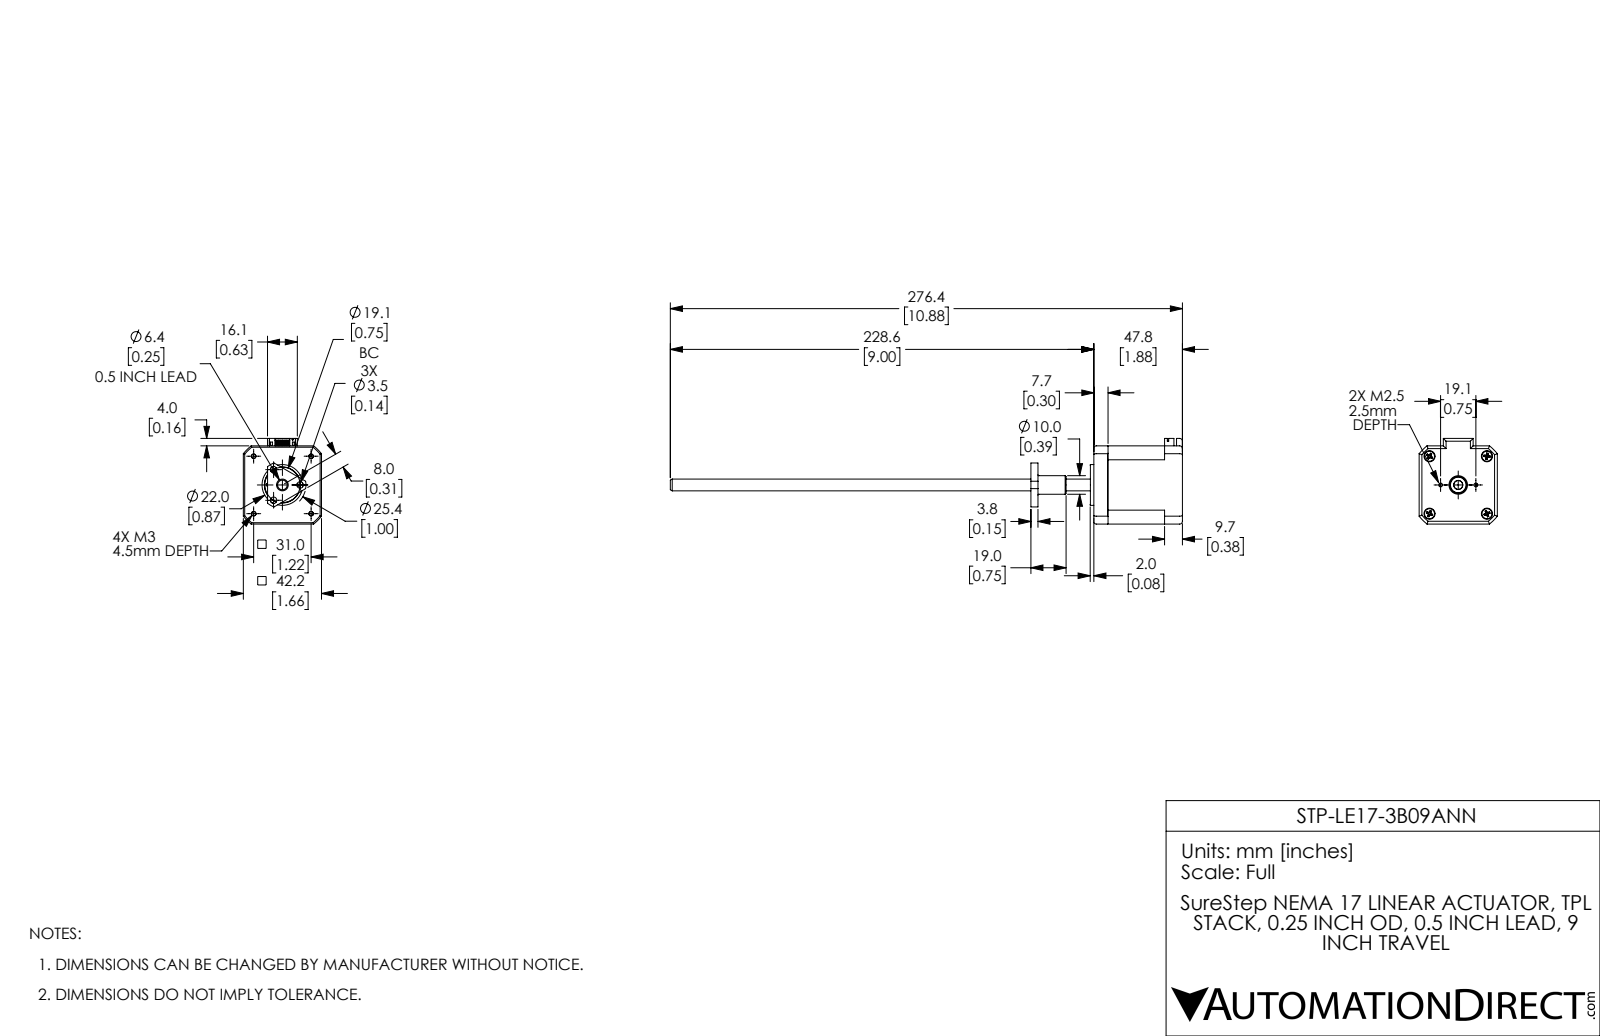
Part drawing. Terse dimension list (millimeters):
name: STP-LE17-3B09ANN_2; STP-LE17-3B09ANN; STP-LE17-3B09ANN_1
written by: SolidWorks 2017 (AUTOMOTIVE_DESIGN)
unit: mm
bodies: 5 solids, 730 faces (364 planar, 236 cylindrical, 130 other)
size: 276.4 × 46.2 × 42.2
volume: 80 510 mm³; area: 29 873 mm²
holes: 4× ⌀2.5, 4× ⌀3.8, 4× ⌀6, 3× ⌀3.5, 2× ⌀1.5, 2× ⌀2.05, 1× ⌀4.9, 1× ⌀13, 1× ⌀17, 1× ⌀19.46, 1× ⌀20
bosses: 4× ⌀5.4, 4× ⌀2.91, 1× ⌀27, 1× ⌀25.91, 1× ⌀22, 1× ⌀12, 1× ⌀10, 1× ⌀9
rounds: 12× R1, 11× R1.5, 2× R2.5, 1× R0.7, 1× R12.7, 1× R14.25, 1× R16, 1× R25.1
face distances: 42.2, 9.65, 47.8, 40.15, 38.15, 1.6, 30.5, 7.65, 45.3, 40.6
hole spacings: 16.61, 9.52, 21.92, 29.43, 31, 4.93, 8, 12.96
